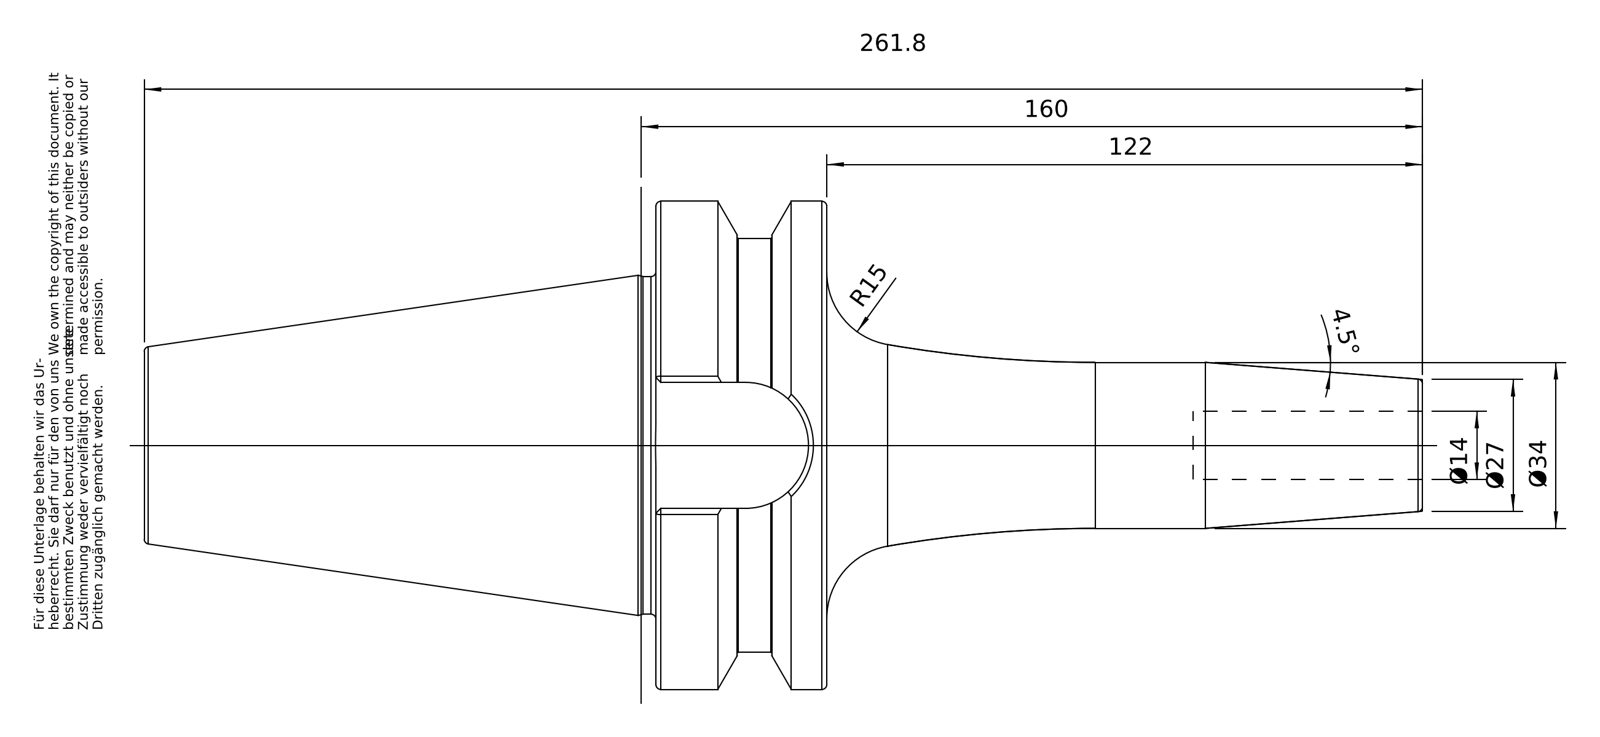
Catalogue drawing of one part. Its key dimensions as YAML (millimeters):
part_name: "50-642-14"
step_written_by: "PRO/ENGINEER BY PARAMETRIC TECHNOLOGY CORPORATION, 2010430 (CONFIG_CONTROL_DESIGN)"
units: millimeters
bodies: {solids: 1, faces: 98, planar: 26, cylindrical: 22, other: 50}
overall_size: [261.8, 99.97, 99.97]
volume: 581896
surface_area: 65589
round_holes:
  - {diameter: 14, count: 1}
  - {diameter: 20.75, count: 1}
  - {diameter: 25.02, count: 1}
  - {diameter: 25.7, count: 1}
round_bosses_or_shafts:
  - {diameter: 99.97, count: 1}
  - {diameter: 84.75, count: 1}
  - {diameter: 69.15, count: 1}
  - {diameter: 34, count: 1}
  - {diameter: 24.01, count: 1}
partial_cylinders:
  - {radius: 12.9, count: 1}
face_to_face_distances: [35, 70.4, 104.8, 139.8, 25.8, 261.8, 157, 122, 214.8, 110]
